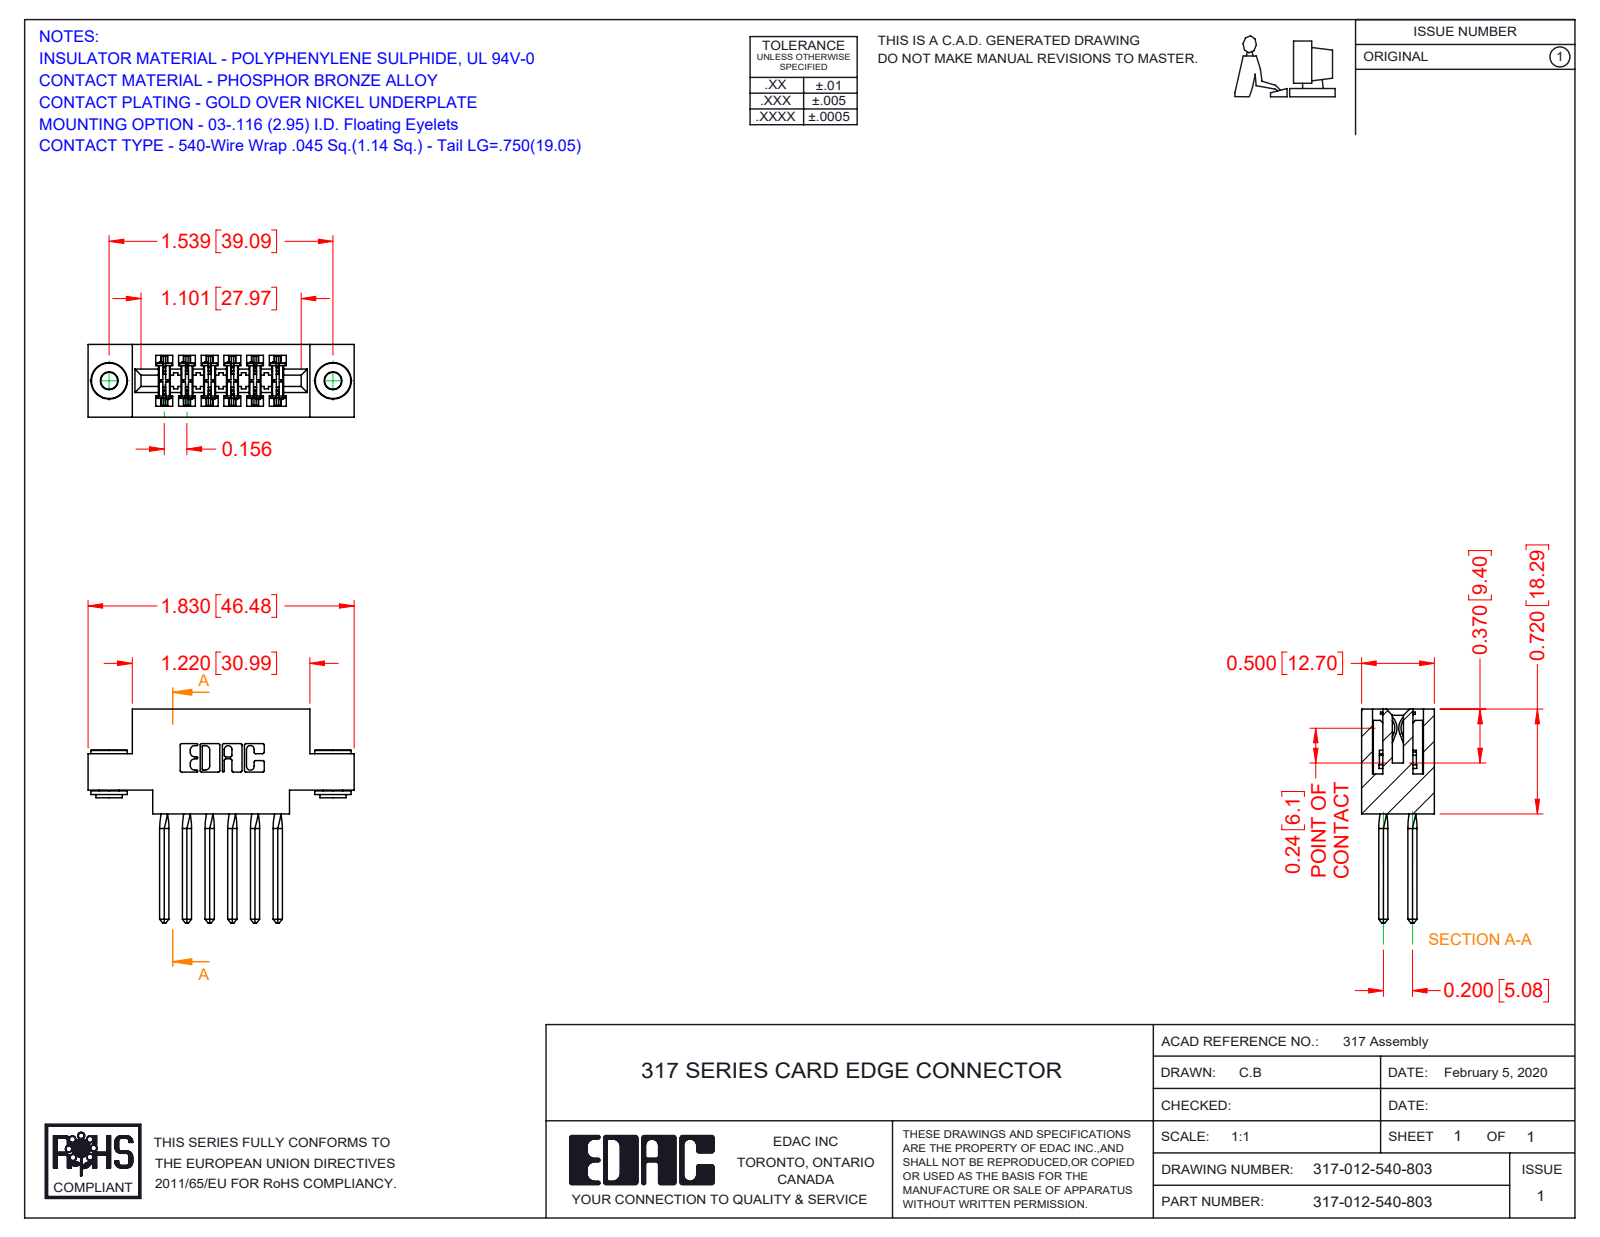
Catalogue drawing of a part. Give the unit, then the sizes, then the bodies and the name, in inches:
Units: inches
Overall size (bounding box): 1.83 × 1.47 × 0.5
Round holes (diameter × count): ⌀0.116 ×2, ⌀0.156 ×2
Round bosses / shafts (diameter × count): ⌀0.25 ×2, ⌀0.18 ×2, ⌀0.136 ×2
Partial cylindrical surfaces — rounded edges, fillets, slot ends (radius × count): R0.015 ×24, R0.01 ×22, R0.007 ×6, R0.031 ×6, R0.026 ×3, R0.095 ×2, R0.1 ×2, R0.11 ×2
Main face-to-face distances: 0.5, 0.11, 0.075, 0.425, 0.22, 0.065, 0.156, 0.116, 0.163, 0.331
Hole centre spacings: 1.539
Volume: 0.403 in³ · Surface area: 13.48 in²
Bodies: 15 solids, 1208 faces (944 planar, 208 cylindrical, 56 other)
Part name (STEP PRODUCT): 345-250-002_345-250-002-102; 317 Part_.156 Dia - TH; 317-290-001_540; 317-012-540-803
STEP written by: SolidWorks 2016 (CONFIG_CONTROL_DESIGN)
